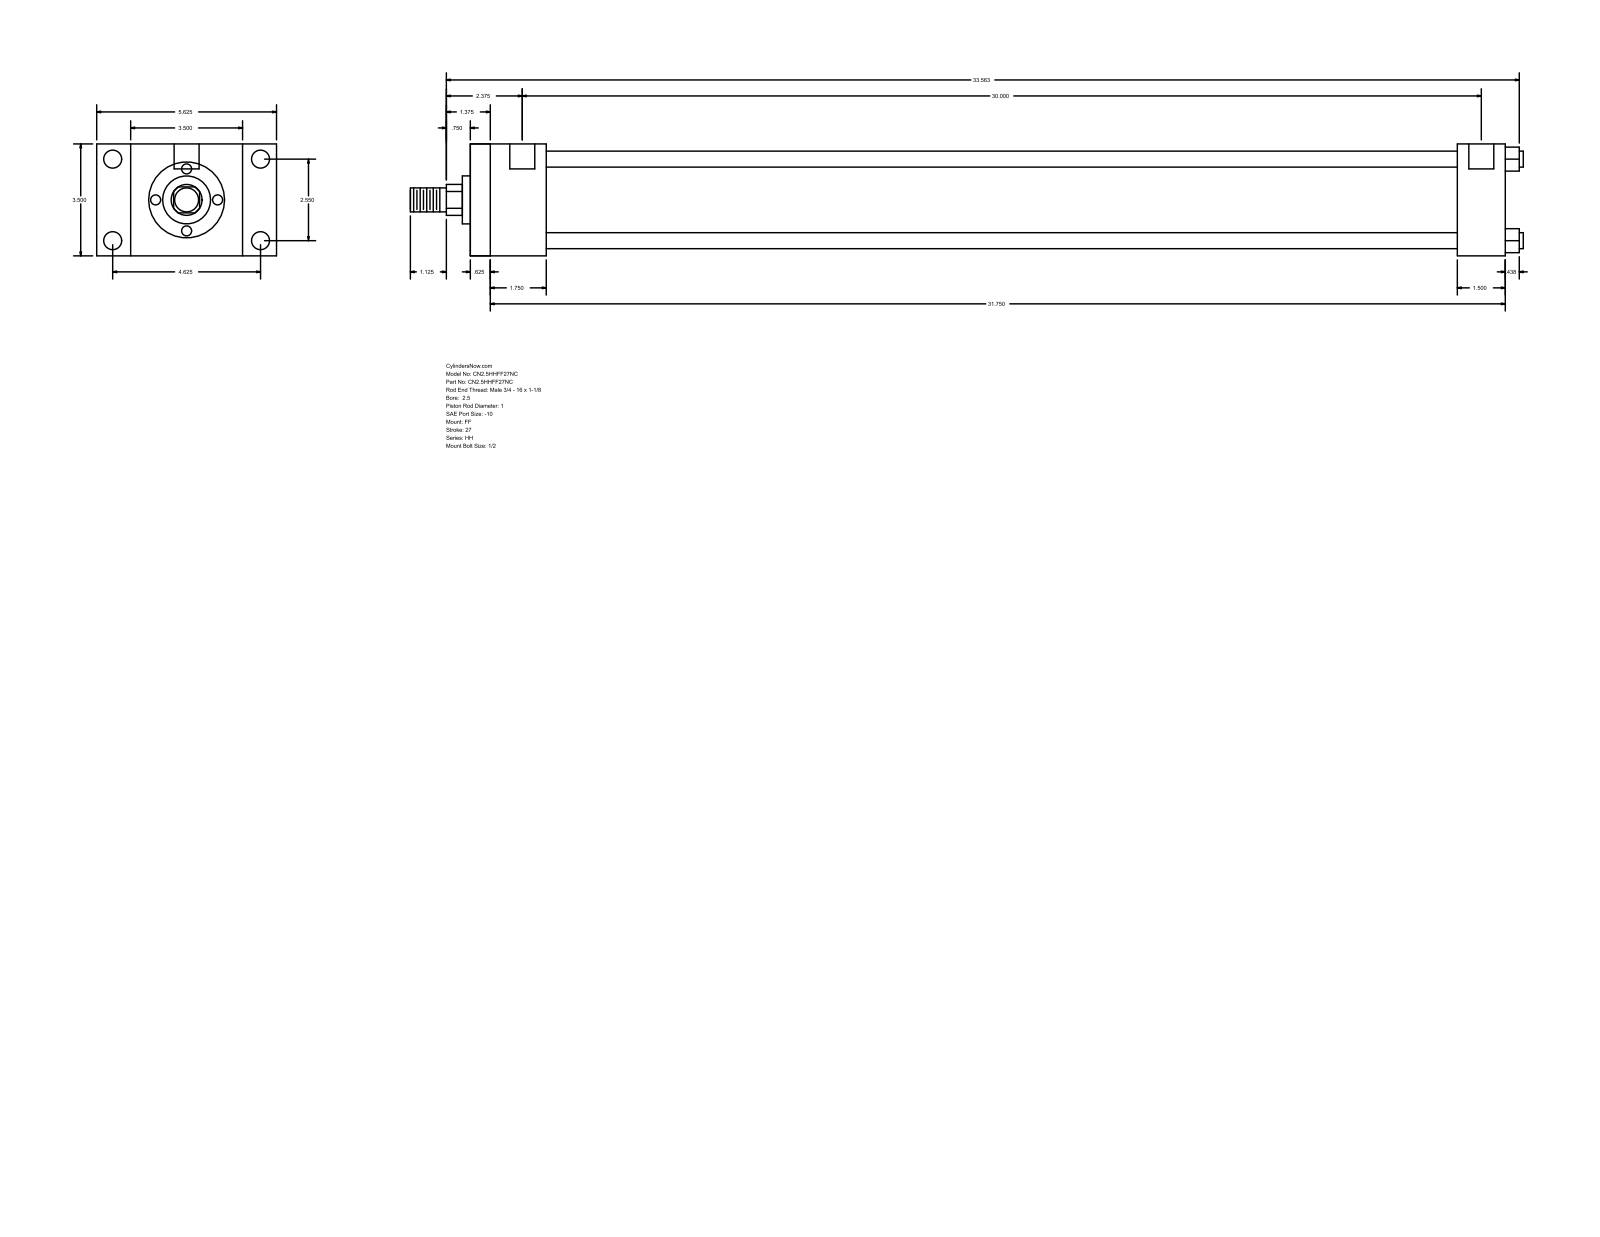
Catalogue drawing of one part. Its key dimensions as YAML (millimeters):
part_name: "HH_FF__0250_1"
step_written_by: "GSSL Pune (CONFIG_CONTROL_DESIGN)"
units: millimeters
bodies: {solids: 0, faces: 92, planar: 64, cylindrical: 28, other: 0}
overall_size: [884.24, 142.88, 88.9]
round_holes:
  - {diameter: 5.56, count: 4}
  - {diameter: 14.3, count: 4}
  - {diameter: 19.84, count: 2}
round_bosses_or_shafts:
  - {diameter: 12.7, count: 4}
  - {diameter: 73.03, count: 1}
  - {diameter: 38.1, count: 1}
  - {diameter: 25.4, count: 1}
  - {diameter: 19.05, count: 1}
partial_cylinders:
  - {radius: 12.29, count: 1}
face_to_face_distances: [88.9, 822.33, 15.87, 806.46, 60.33, 44.46, 762, 784.22, 768.35, 723.89]
hole_center_spacings: [64.76, 117.48, 134.15, 765.17, 1.58, 1.59, 762, 763.58]
